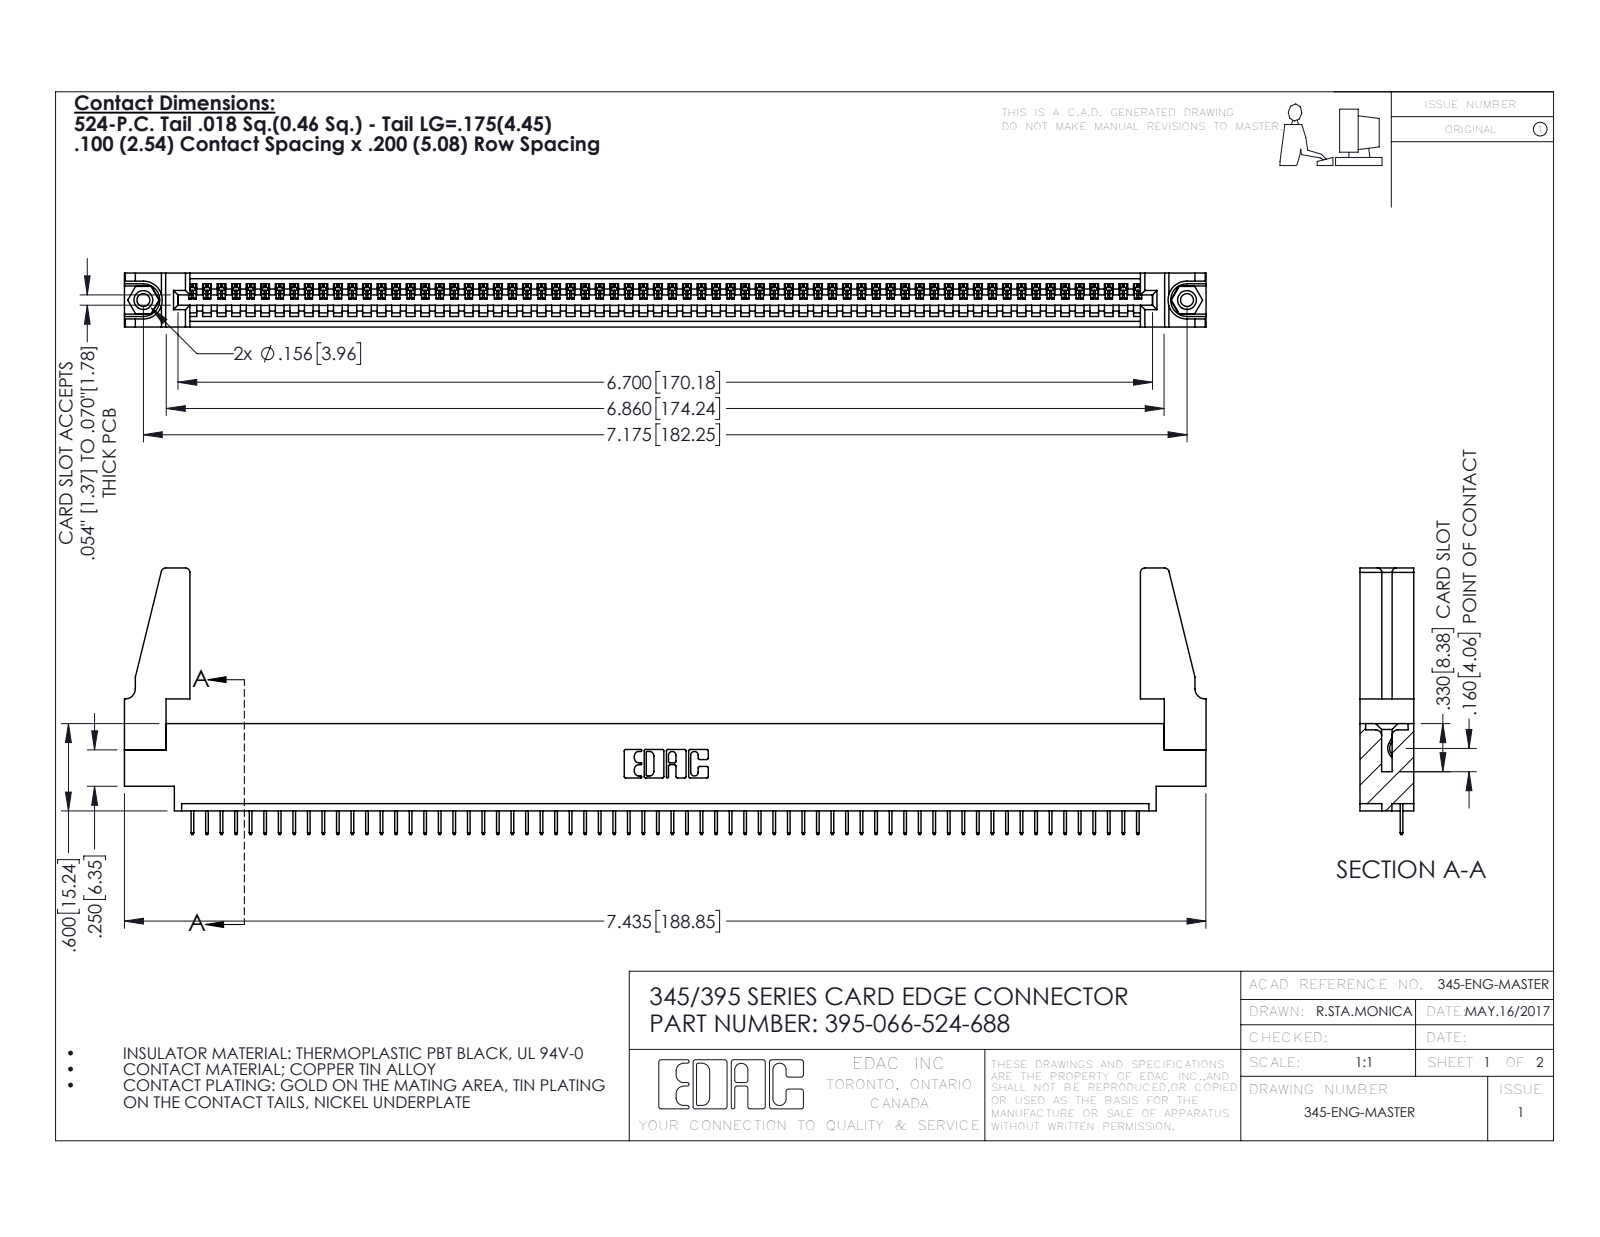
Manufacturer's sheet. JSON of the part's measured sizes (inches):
{"part_name": "345-250-001_345-250-001-102; 345-292-001_345-293-124; 345-220-078_345-220-088; 345 Part_0.170 Offset - 0.156 Dia-TH (+1 more)", "step_written_by": "SolidWorks 2016 (CONFIG_CONTROL_DESIGN)", "units": "inches", "bodies": {"solids": 71, "faces": 4346, "planar": 3192, "cylindrical": 1138, "other": 16}, "overall_size": [7.436, 1.832, 0.37], "volume_in3": 1.282, "surface_area_in2": 40.85, "round_holes": [[0.089, 2], [0.125, 2], [0.156, 2], [0.064, 1]], "round_bosses_or_shafts": [[0.155, 2]], "partial_cylinders_radius": [[0.006, 132], [0.01, 22], [0.03, 8], [0.007, 6], [0.031, 6], [0.026, 3], [0.031, 2], [0.04, 2]], "face_to_face_distances": [0.072, 0.298, 0.37, 0.098, 0.272, 0.025, 0.2, 0.225, 0.072, 0.175], "hole_center_spacings": [0.27, 6.939, 7.175]}
